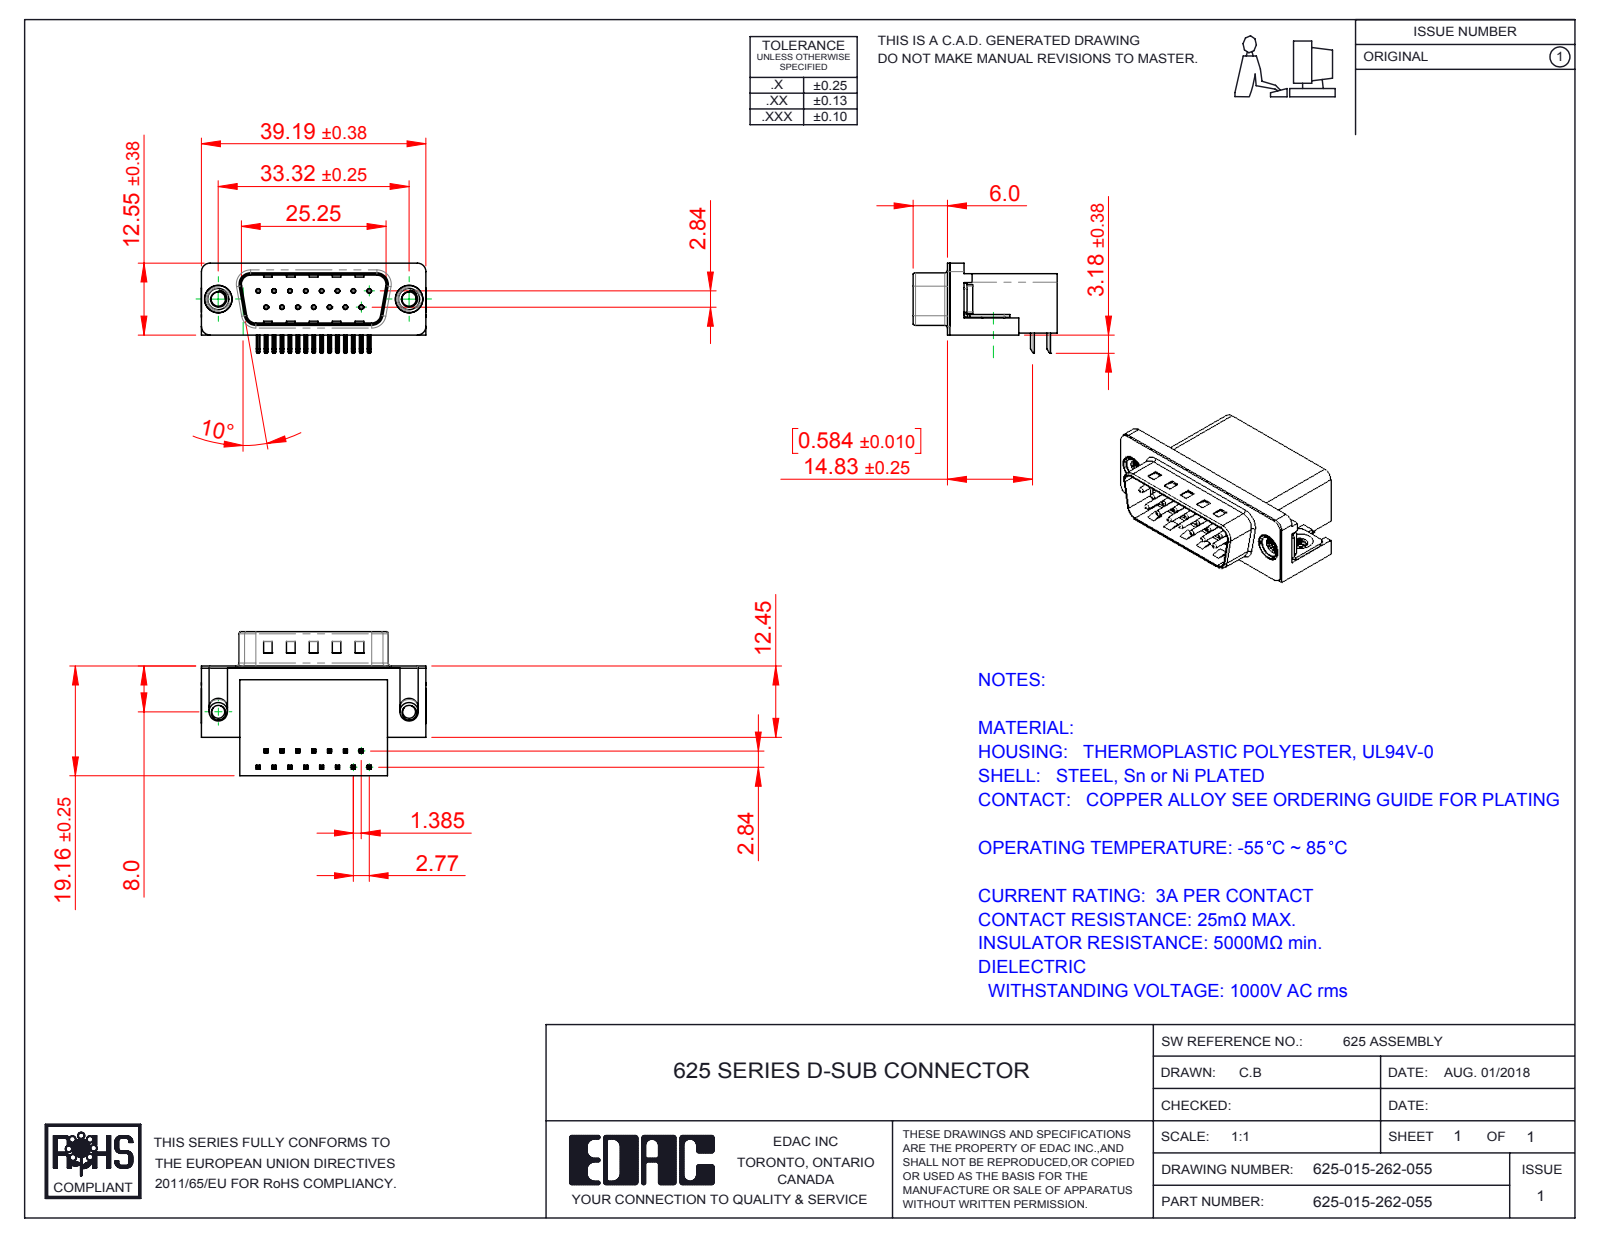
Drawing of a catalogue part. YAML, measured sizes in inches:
part_name: "625 Housing_15 Socket; 625 Contact Top; 625 M3 Threaded Rivet; 625-015-262-055 (+3 more)"
step_written_by: "SolidWorks 2016 (CONFIG_CONTROL_DESIGN)"
units: inches
bodies: {solids: 21, faces: 1511, planar: 895, cylindrical: 463, other: 153}
overall_size: [1.544, 0.991, 0.619]
volume: 0.381
surface_area: 10.09
round_holes:
  - {diameter: 0.014, count: 15}
  - {diameter: 0.031, count: 15}
  - {diameter: 0.089, count: 2}
  - {diameter: 0.098, count: 2}
  - {diameter: 0.157, count: 2}
  - {diameter: 0.189, count: 2}
  - {diameter: 0.197, count: 2}
round_bosses_or_shafts:
  - {diameter: 0.03, count: 15}
  - {diameter: 0.193, count: 2}
  - {diameter: 0.187, count: 2}
  - {diameter: 0.154, count: 2}
  - {diameter: 0.128, count: 2}
partial_cylinders:
  - {radius: 0.01, count: 68}
  - {radius: 0.005, count: 30}
  - {radius: 0.039, count: 16}
  - {radius: 0.02, count: 9}
  - {radius: 0.063, count: 8}
  - {radius: 0.059, count: 6}
  - {radius: 0.035, count: 4}
  - {radius: 0.079, count: 4}
face_to_face_distances: [0.016, 0.407, 0.739, 0.083, 0.412, 0.754, 0.067, 0.428, 0.345, 0.64]
hole_center_spacings: [0.124, 0.109, 0.218, 0.327, 0.436, 0.198, 0.198, 0.294]
